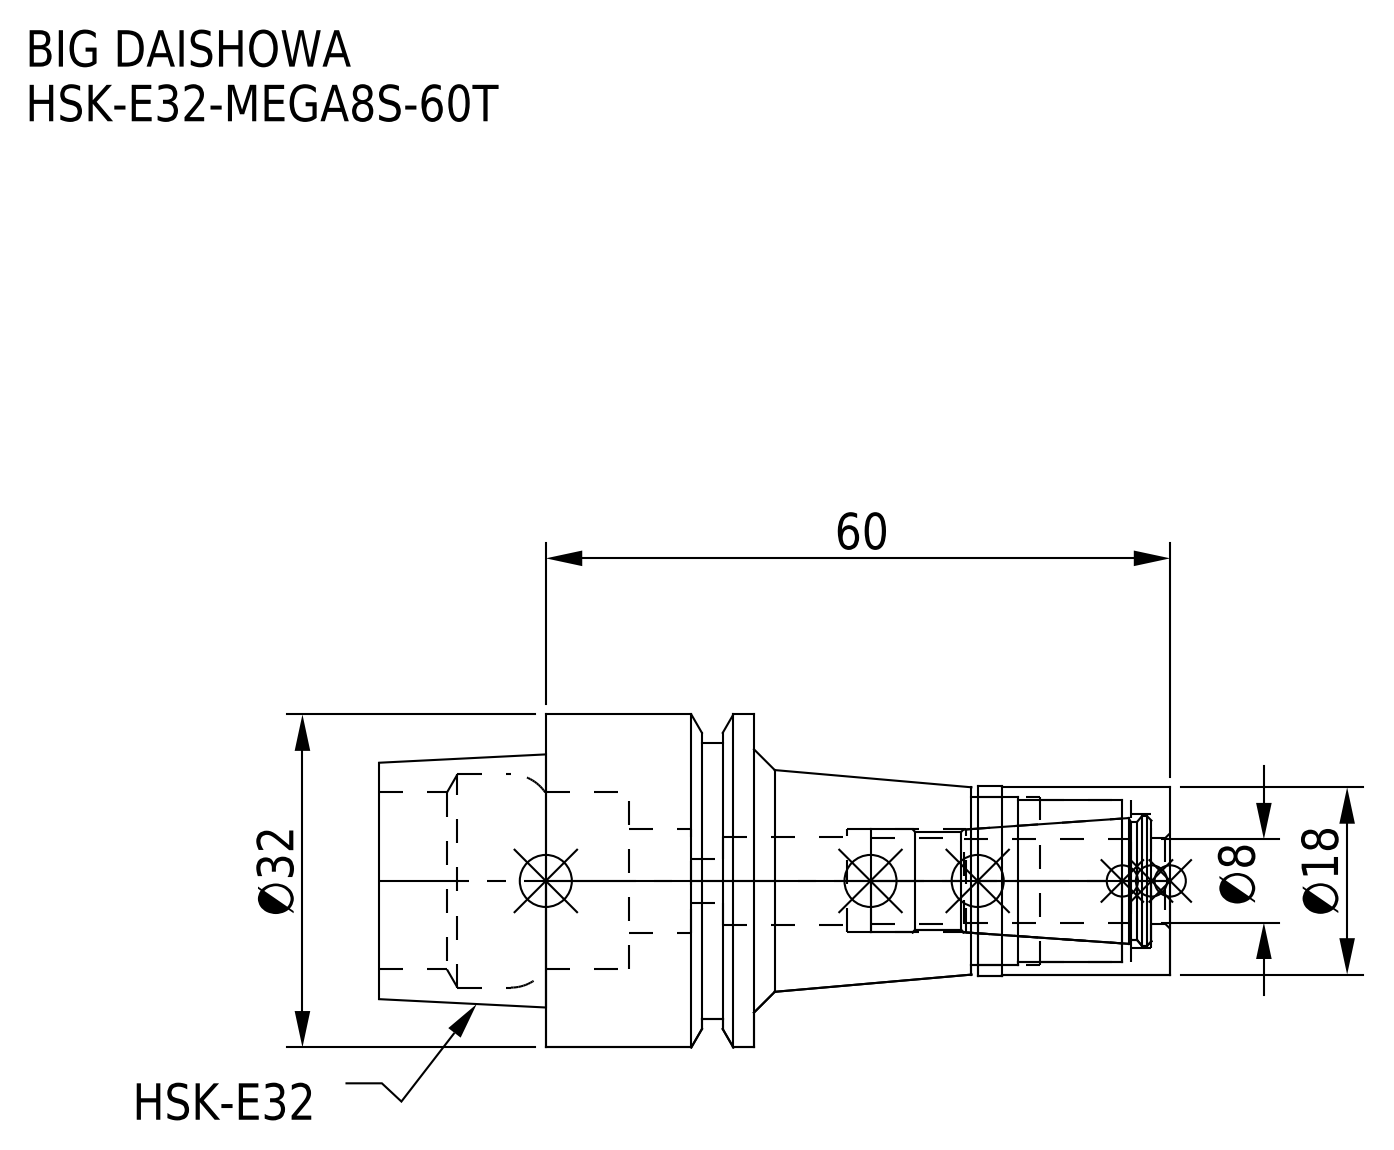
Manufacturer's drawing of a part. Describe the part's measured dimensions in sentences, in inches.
The part is named "DXF_TEMP_ASSY_ASM_4_ASM.stp; MGN8S_1.stp; HSK-E32-MEGA8S-60T-080.stp; HE32MS08060T-080_ASM.stp (+3 more)". Its 3-D file was written by "SolidWorks 2019 (CONFIG_CONTROL_DESIGN)". It is 2 solids with 74 faces: 18 planar, 38 cylindrical and 18 other. Overall it measures 2.992 by 1.26 by 1.26 inches. Its volume is 1.437 cubic inches and its surface area 18.67 square inches. Round holes: 1 of diameter 0.165, 1 of diameter 0.323, 1 of diameter 0.331, 1 of diameter 0.39, 1 of diameter 0.394, 1 of diameter 0.508, 1 of diameter 0.614, 1 of diameter 0.634, 1 of diameter 0.669, 1 of diameter 0.807. Round bosses or shafts: 1 of diameter 1.26, 1 of diameter 1.043, 1 of diameter 0.72, 1 of diameter 0.709. The main face-to-face distances are 0.787, 1.575, 2.362, 2.992, 1.417, 0.63, 2.049, 0.474, 0.313, 0.943.
